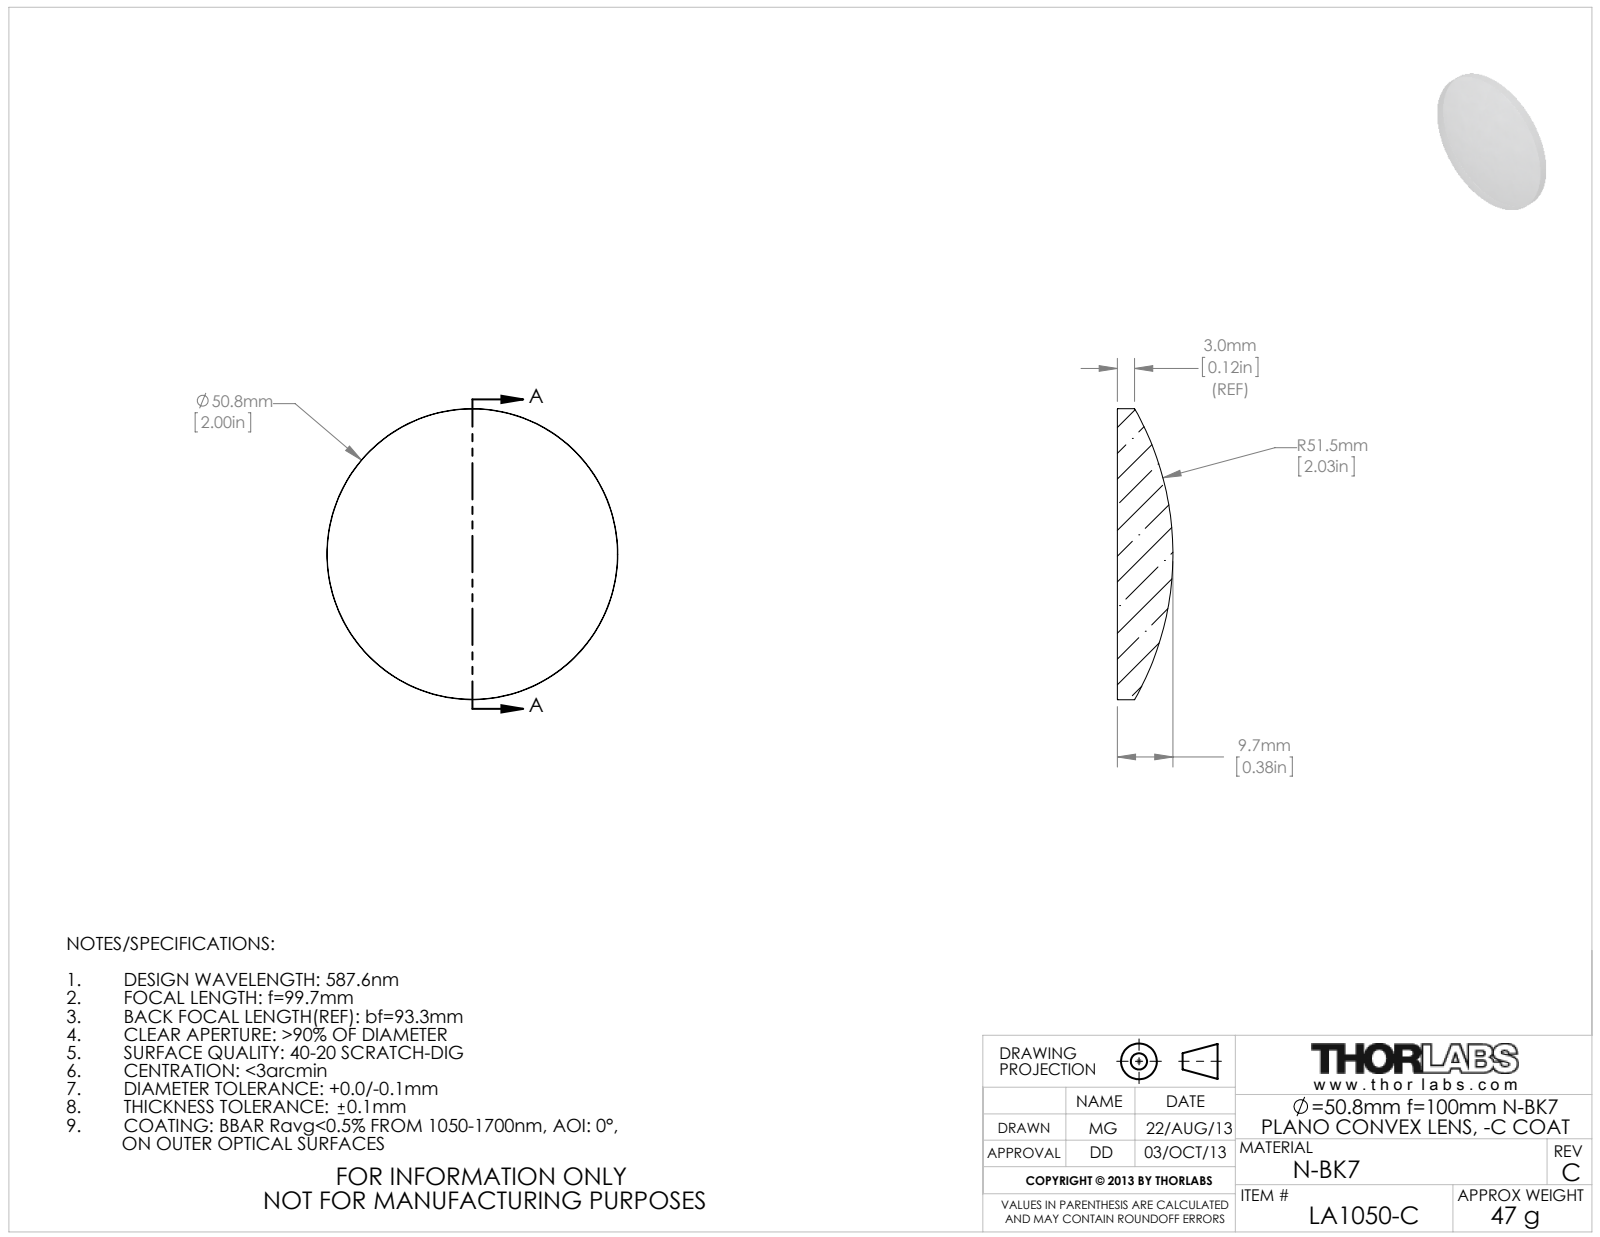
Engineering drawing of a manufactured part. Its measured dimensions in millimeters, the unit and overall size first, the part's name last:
Units: millimetres
Overall size (bounding box): 50.8 × 50.8 × 9.69
Round bosses / shafts (diameter × count): ⌀50.8 ×1
Bodies: 0 solids, 5 faces (1 planar, 2 cylindrical, 2 other)
Part name (STEP PRODUCT): 4602-E0W
STEP written by: SolidWorks 2009 (AUTOMOTIVE_DESIGN)
